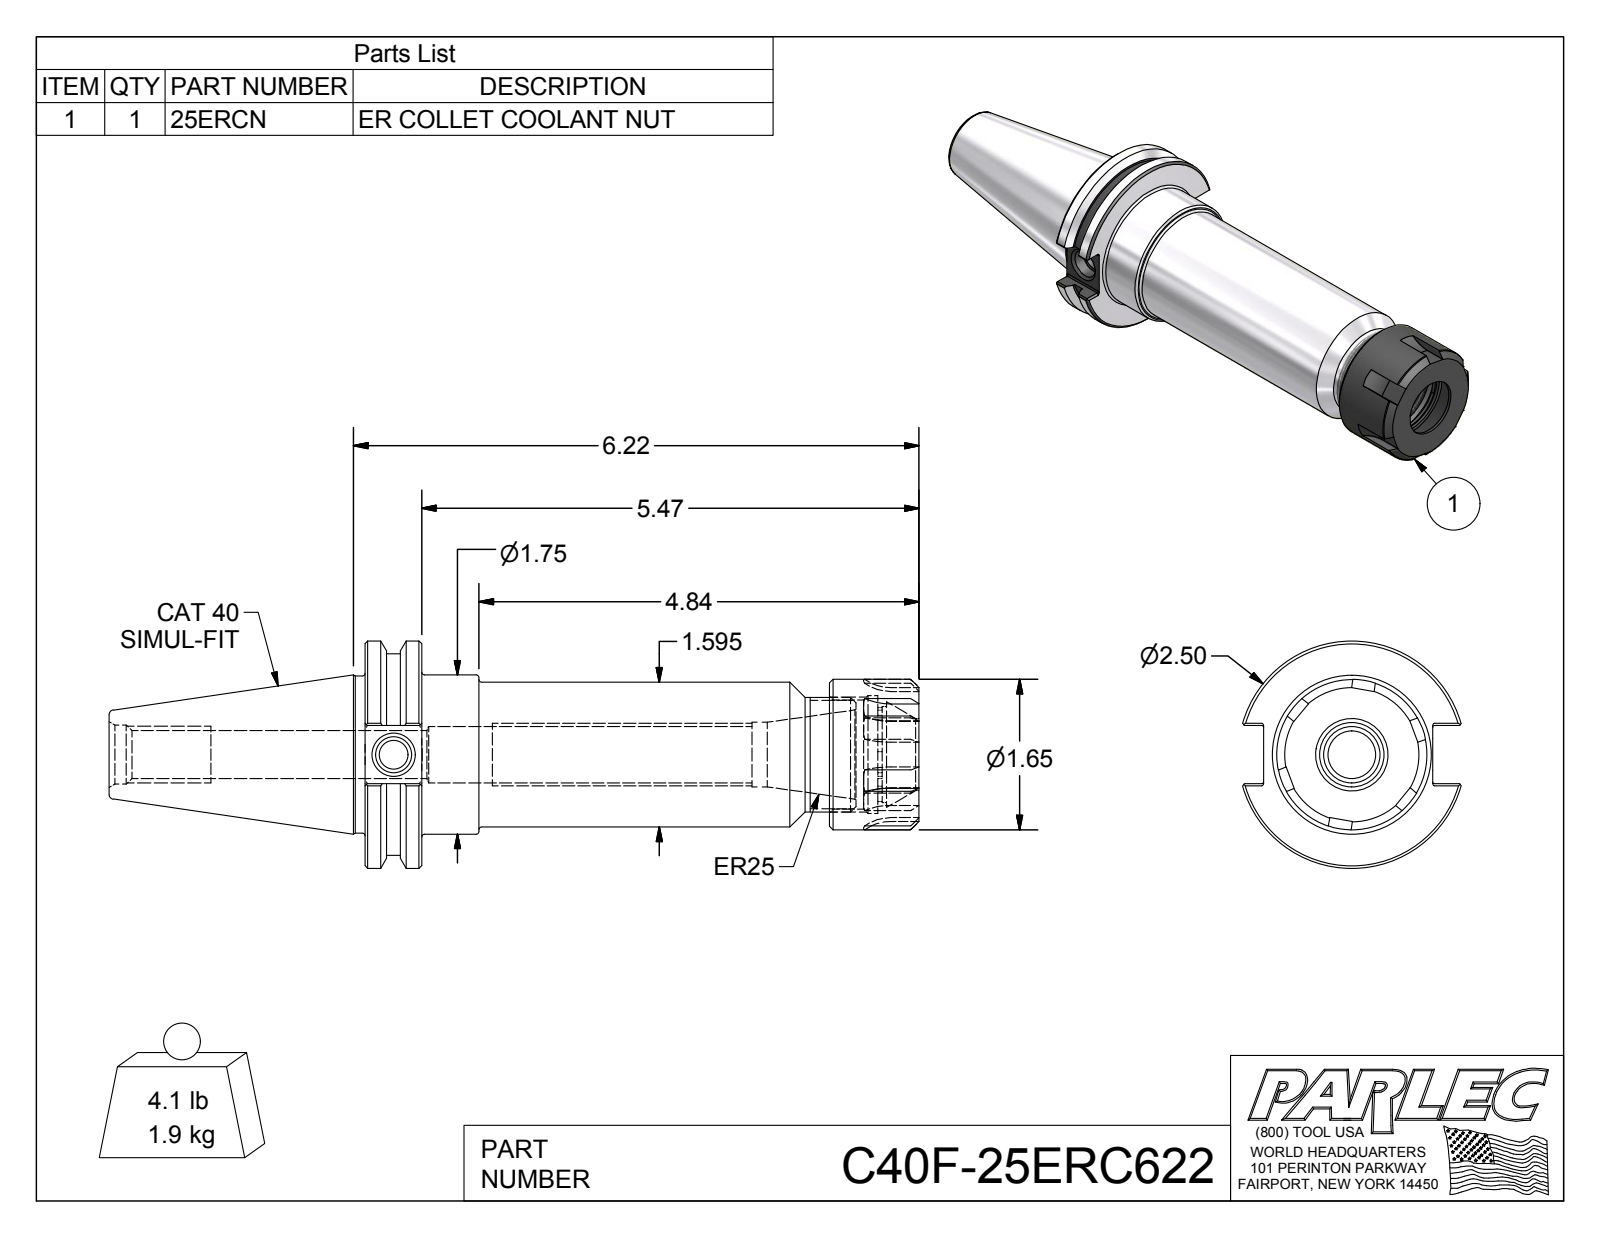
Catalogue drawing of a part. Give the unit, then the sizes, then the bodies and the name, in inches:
Units: inches
Overall size (bounding box): 8.908 × 2.5 × 2.403
Round holes (diameter × count): ⌀0.315 ×1, ⌀0.399 ×1, ⌀0.527 ×1, ⌀0.62 ×1, ⌀0.648 ×1, ⌀0.71 ×1, ⌀0.794 ×1, ⌀1.057 ×1, ⌀1.201 ×1, ⌀1.294 ×1
Round bosses / shafts (diameter × count): ⌀2.5 ×1, ⌀2.219 ×1, ⌀1.75 ×1, ⌀1.73 ×1, ⌀1.654 ×1, ⌀1.595 ×1, ⌀1.26 ×1
Partial cylindrical surfaces — rounded edges, fillets, slot ends (radius × count): R0.02 ×12, R0.5 ×6, R0.472 ×1, R0.515 ×1
Main face-to-face distances: 0.625, 6.095, 5.47, 5.111, 4.486, 0.984, 5.642, 5.017, 0.531, 0.453
Volume: 14.76 in³ · Surface area: 75.87 in²
Bodies: 2 solids, 145 faces (61 planar, 44 cylindrical, 40 other)
Part name (STEP PRODUCT): C40F-25ERC622; C40F-25ER6-1; 25ERCN
STEP written by: Autodesk Inventor 2012 (AUTOMOTIVE_DESIGN)
